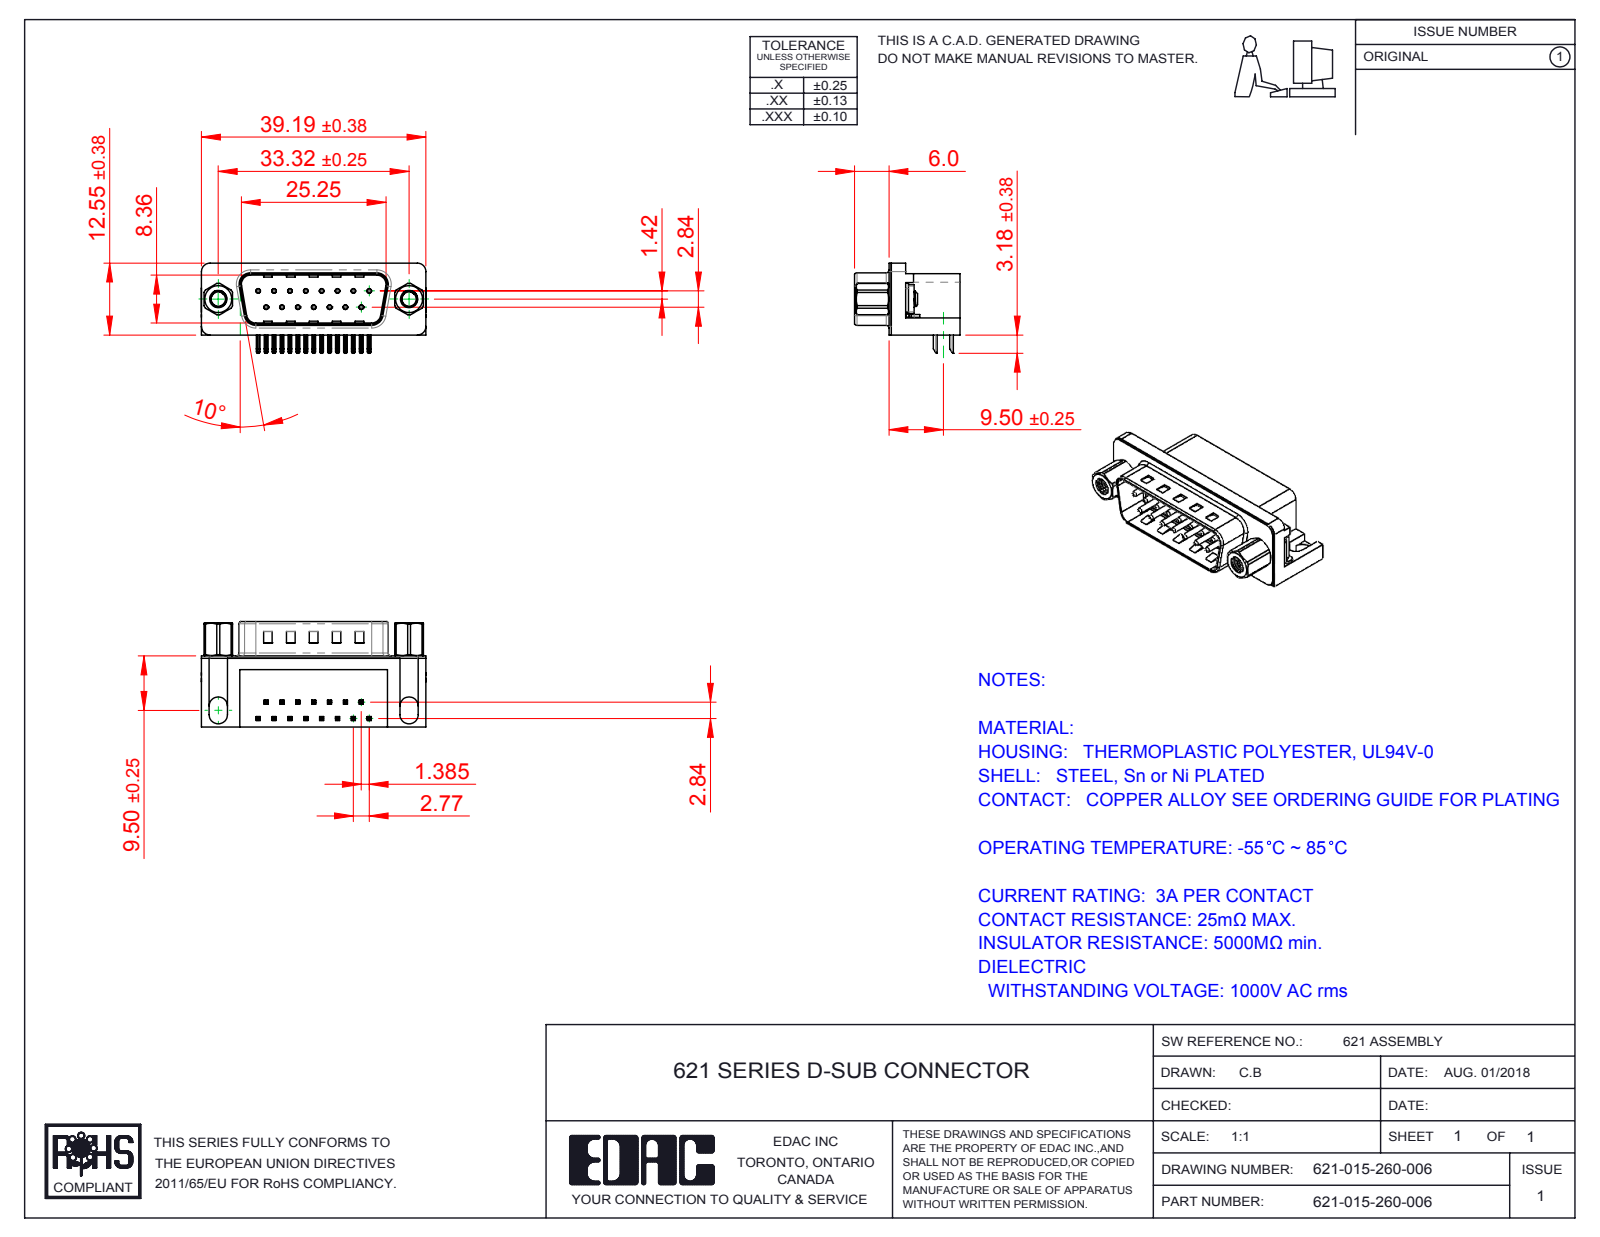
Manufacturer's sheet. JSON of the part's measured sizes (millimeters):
{"part_name": "621 Housing_15 Socket; 621 Contact Bottom; 621 Contact Top; 621 Non Board Mount (+4 more)", "step_written_by": "SolidWorks 2016 (CONFIG_CONTROL_DESIGN)", "units": "millimeters", "bodies": {"solids": 23, "faces": 1619, "planar": 913, "cylindrical": 537, "other": 169}, "overall_size": [39.22, 18.4, 15.73], "volume_mm3": 4618, "surface_area_mm2": 6010, "round_holes": [[0.35, 15], [0.8, 15], [2.5, 2], [4, 2], [4.8, 2], [5, 2]], "round_bosses_or_shafts": [[0.75, 15], [4.9, 2], [4.75, 2], [3.9, 2], [3, 2]], "partial_cylinders_radius": [[0.25, 68], [0.12, 30], [1, 16], [0.5, 9], [1.6, 8], [1.5, 6], [0.9, 4], [2, 4]], "face_to_face_distances": [0.4, 12, 10.35, 12.4, 2.1, 10.46, 1.7, 10.86, 8.76, 9.5], "hole_center_spacings": [3.16, 2.77, 5.54, 8.31, 11.08, 5.03, 5.04, 7.48]}
